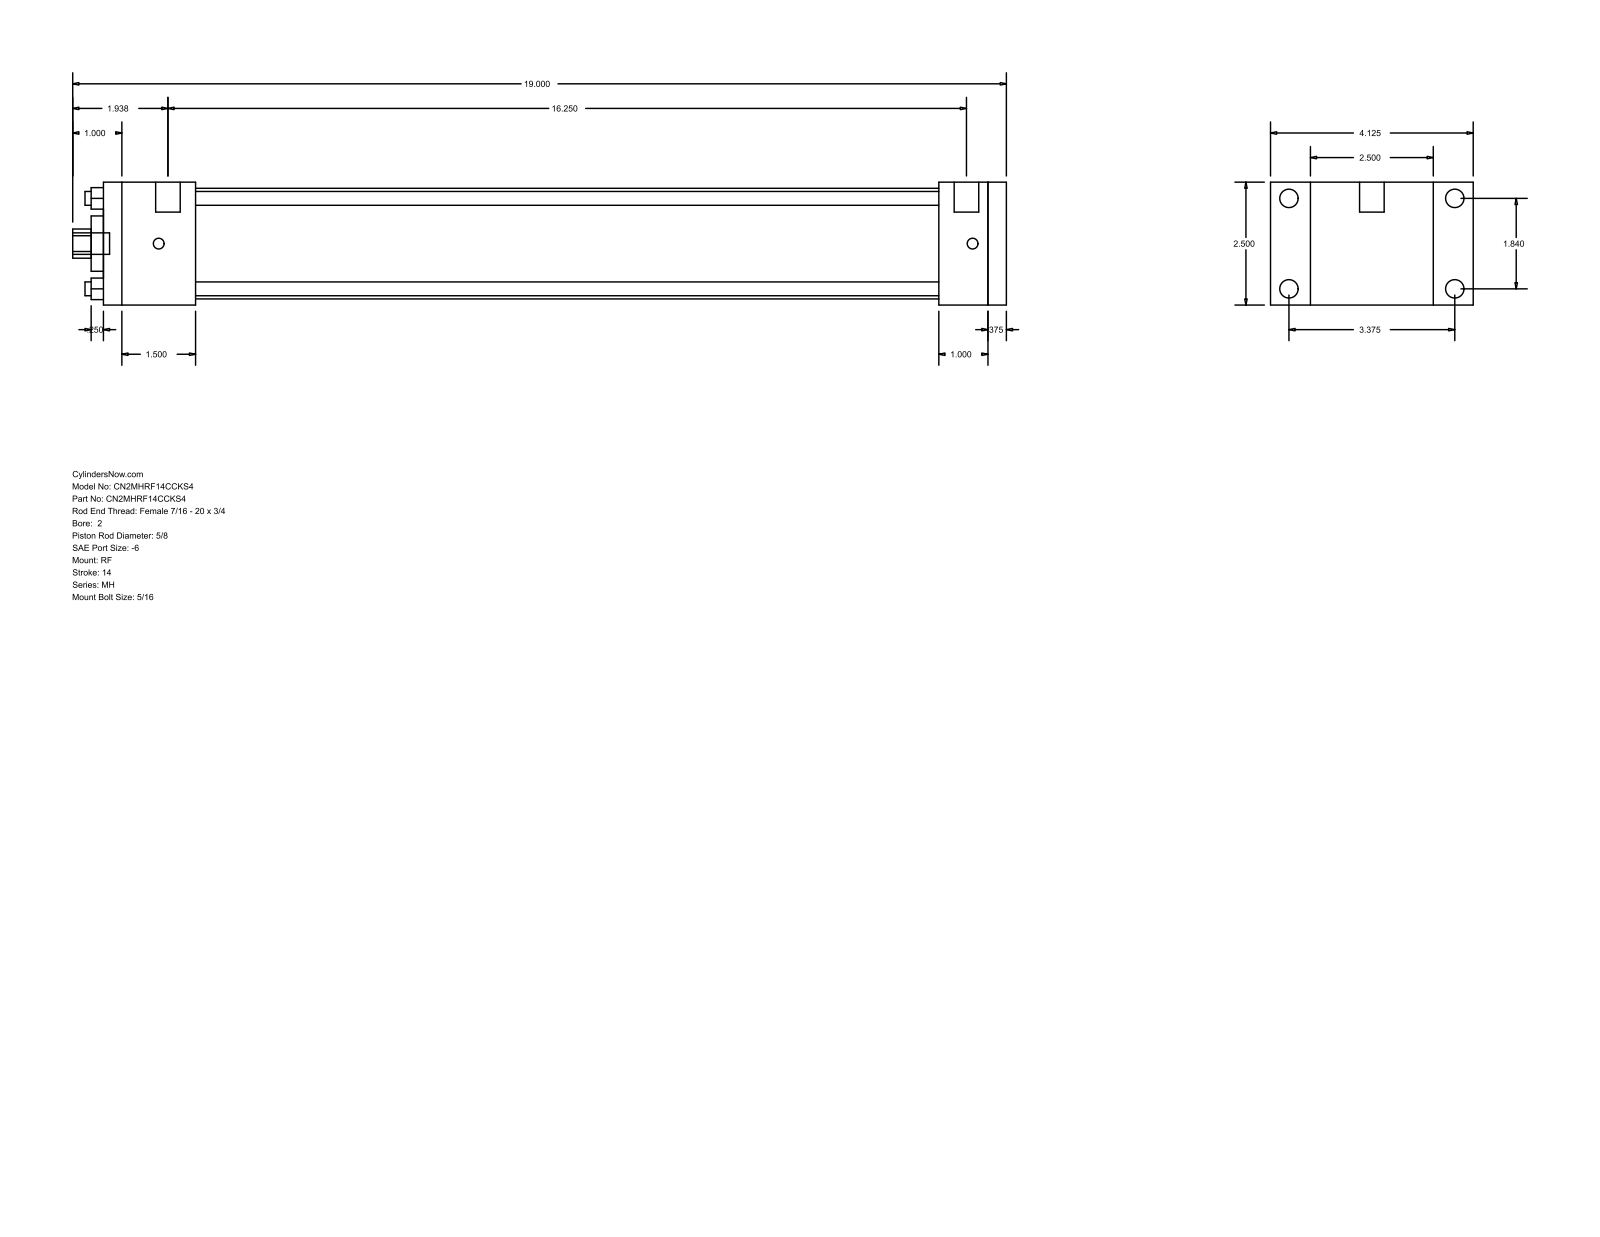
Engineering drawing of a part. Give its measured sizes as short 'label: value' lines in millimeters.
name: MH_RF__0200_0.625
written by: GSSL Pune (CONFIG_CONTROL_DESIGN)
unit: mm
bodies: 0 solids, 92 faces (64 planar, 28 cylindrical, 0 other)
size: 482.6 × 104.78 × 63.5
holes: 4× ⌀7.14, 1× ⌀15.88, 1× ⌀28.57, 1× ⌀57.15
bosses: 4× ⌀9.53, 4× ⌀5.56, 2× ⌀12.7, 1× ⌀11.11
rounds: 1× R7.54
face distances: 63.5, 466.72, 9.53, 457.19, 47.62, 431.8, 384.18, 409.57, 419.1, 25.39
hole spacings: 33.05, 46.74, 66.1
